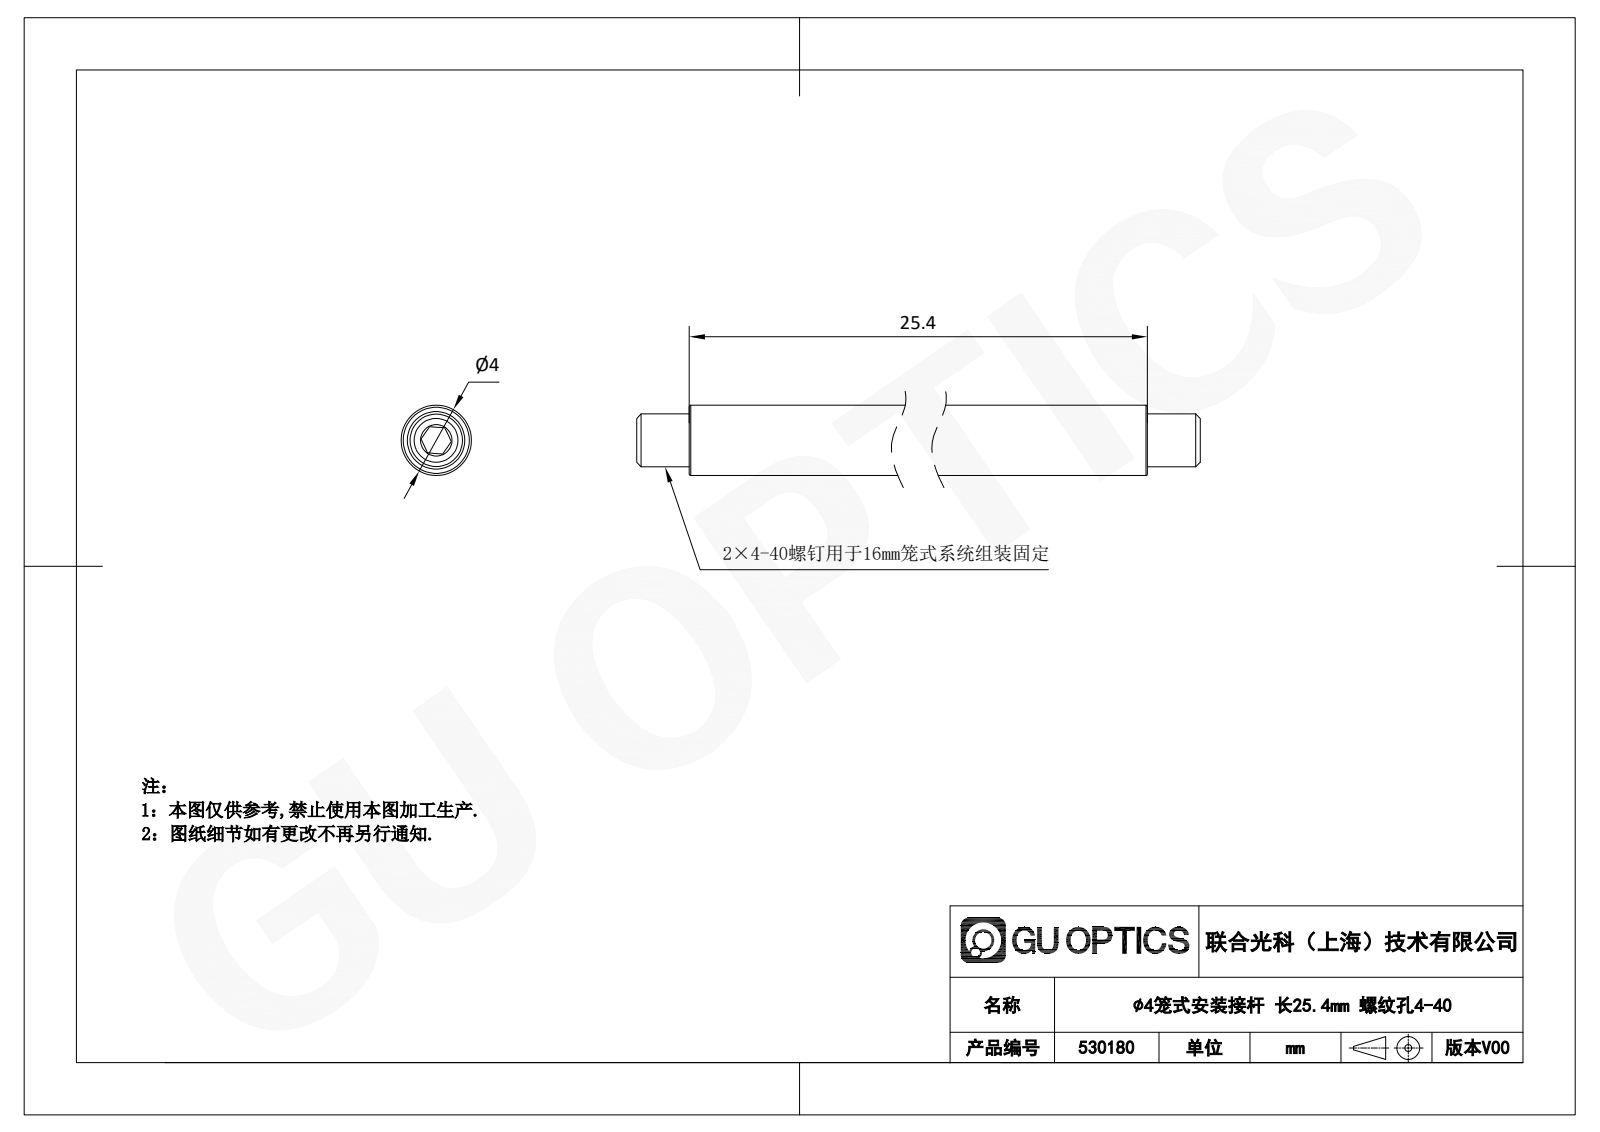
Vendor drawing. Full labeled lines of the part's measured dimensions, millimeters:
Part name (STEP PRODUCT): 530180
STEP written by: SolidWorks 2020 (CONFIG_CONTROL_DESIGN)
Units: millimetres
Bodies: 3 solids, 37 faces (20 planar, 5 cylindrical, 12 other)
Overall size (bounding box): 35.4 × 4 × 4
Volume: 369 mm³ · Surface area: 609 mm²
Round holes (diameter × count): ⌀2.5 ×1
Round bosses / shafts (diameter × count): ⌀4 ×1, ⌀3 ×1
Main face-to-face distances: 3, 22.4, 5, 8, 27.4, 30.4, 1.5, 25.4, 1, 34.4
